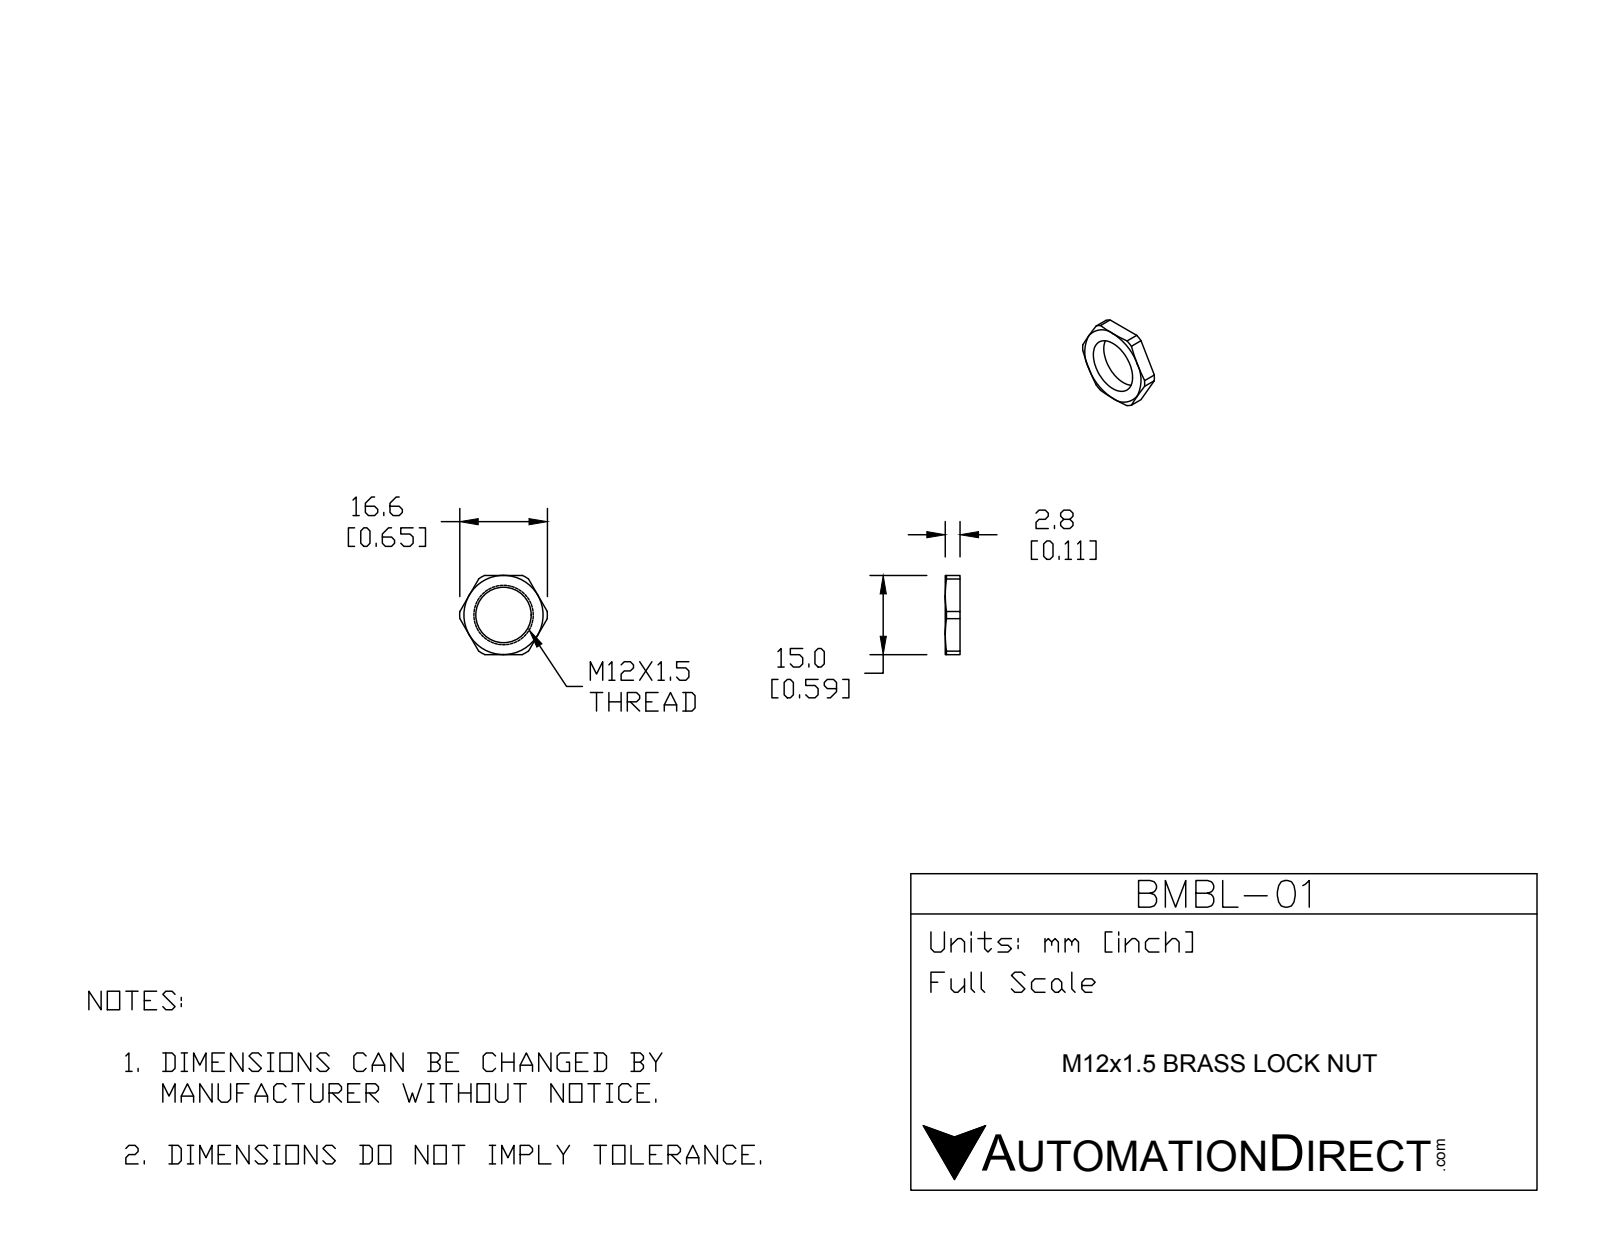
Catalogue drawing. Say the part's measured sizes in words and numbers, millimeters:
The part is named "BMBL-01". Its 3-D file was written by "SolidWorks 2015 (CONFIG_CONTROL_DESIGN)". It is 1 solid with 23 faces: 8 planar, 9 cylindrical and 6 other. Overall it measures 16.6 by 15 by 2.8 millimeters. Its volume is 298 cubic millimeters and its surface area 444 square millimeters. Round holes: 1 of diameter 10.5. Partial cylindrical surfaces (rounded edges, fillets, slot ends): 1 of radius 8.3. The main face-to-face distances are 2.8, 15.
